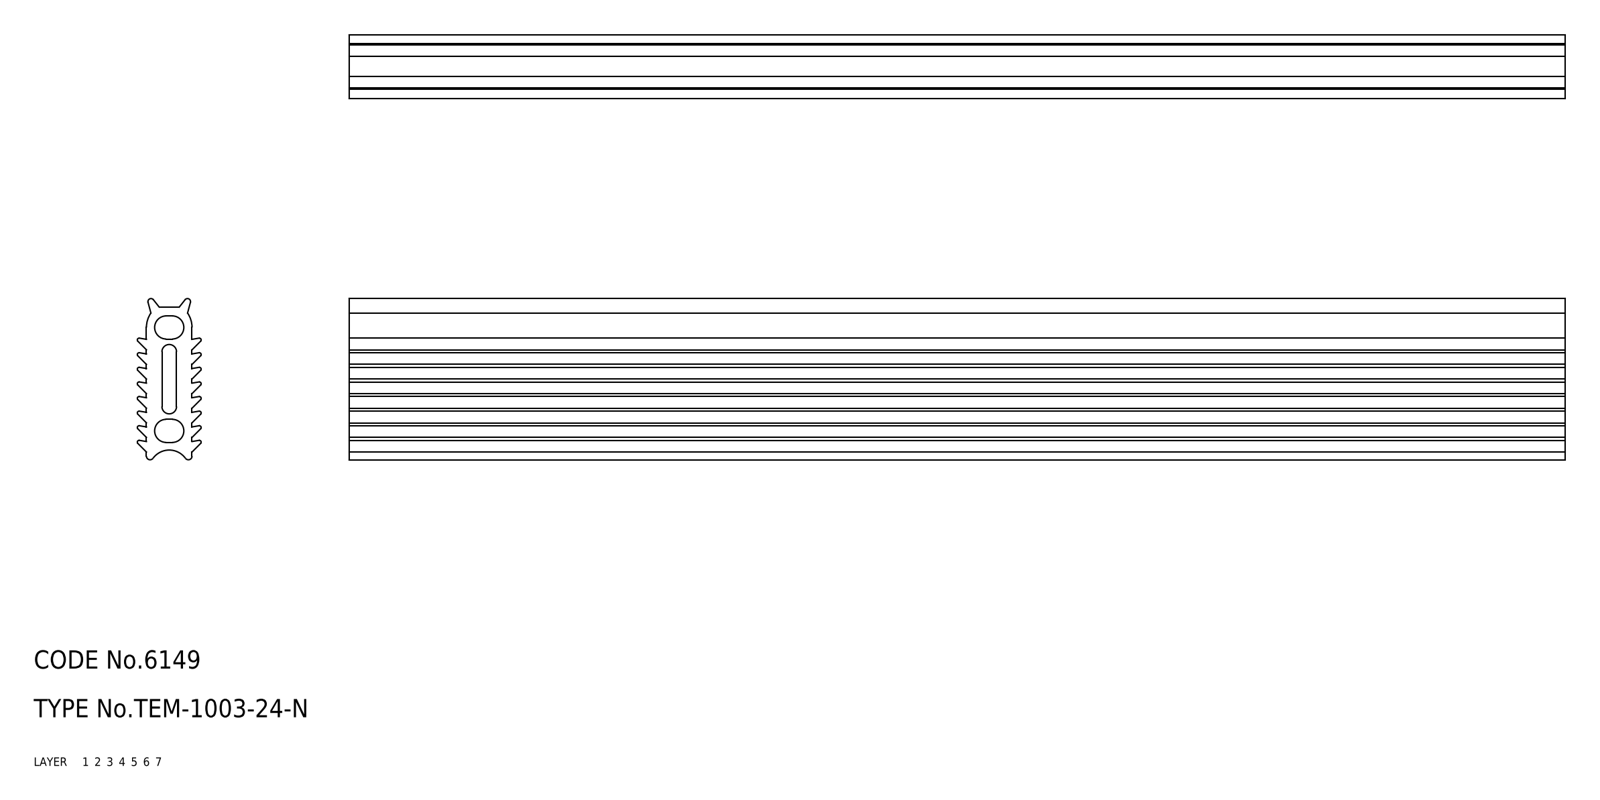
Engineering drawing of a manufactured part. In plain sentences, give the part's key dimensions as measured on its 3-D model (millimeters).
The part is named "gasket". Its 3-D file was written by "CADfix (AUTOMOTIVE_DESIGN)". It is 1 solid with 92 faces: 0 planar, 0 cylindrical and 92 other. Overall it measures 200 by 26.5 by 10.5 millimeters. Its volume is 30 447 cubic millimeters and its surface area 31 877 square millimeters.
